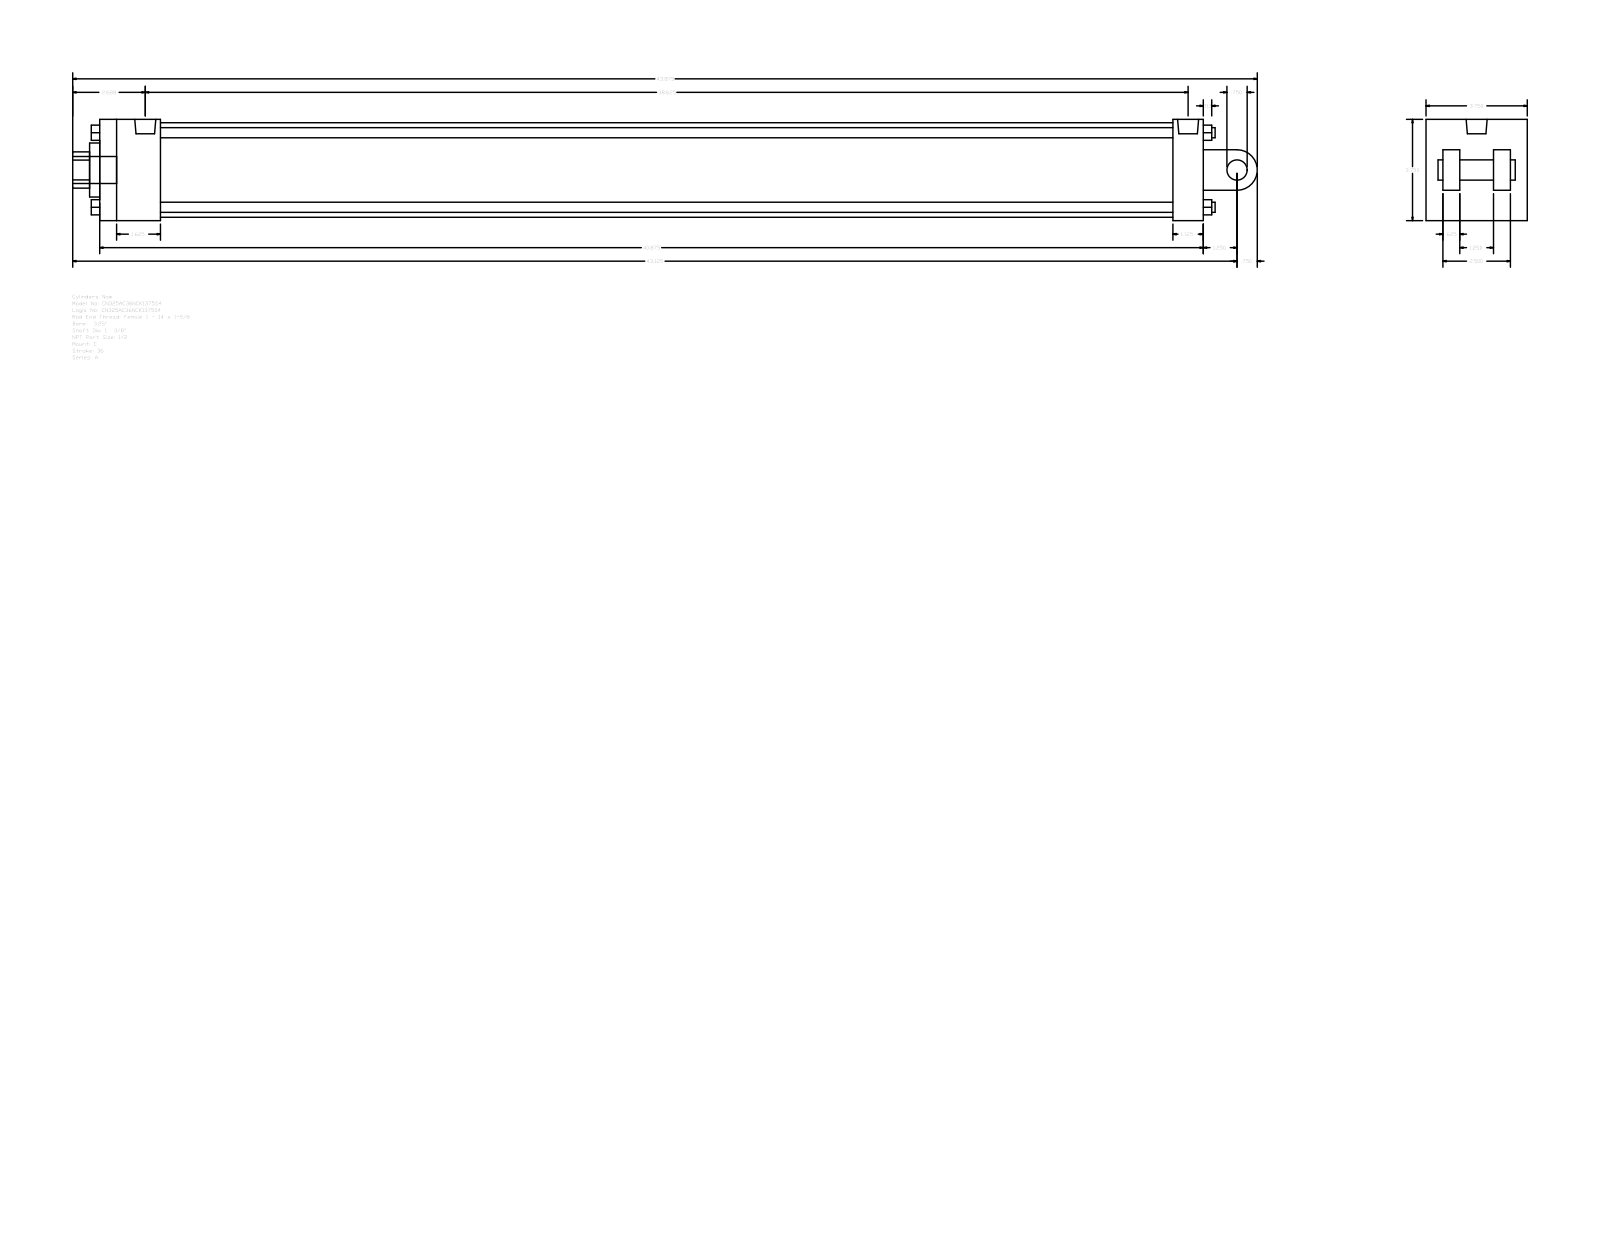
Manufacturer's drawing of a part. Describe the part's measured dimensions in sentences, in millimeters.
The part is named "A_C__0325_1.375". Its 3-D file was written by "GSSL Pune (CONFIG_CONTROL_DESIGN)". It is 0 solids with 135 faces: 102 planar, 33 cylindrical and 0 other. Overall it measures 1114.42 by 95.25 by 95.25 millimeters. Round holes: 2 of diameter 8.73, 1 of diameter 19.77, 1 of diameter 34.92, 1 of diameter 50.8, 1 of diameter 88.9. Round bosses or shafts: 4 of diameter 9.53, 2 of diameter 8.73, 1 of diameter 25.4, 1 of diameter 19.77, 1 of diameter 19.05. Partial cylindrical surfaces (rounded edges, fillets, slot ends): 1 of radius 17.06, 1 of radius 19.05. The main face-to-face distances are 95.24, 15.87, 1038.22, 28.57, 63.5, 66.67, 31.74, 79.37, 47.63, 1009.65. The hole center spacings are 3.18.
